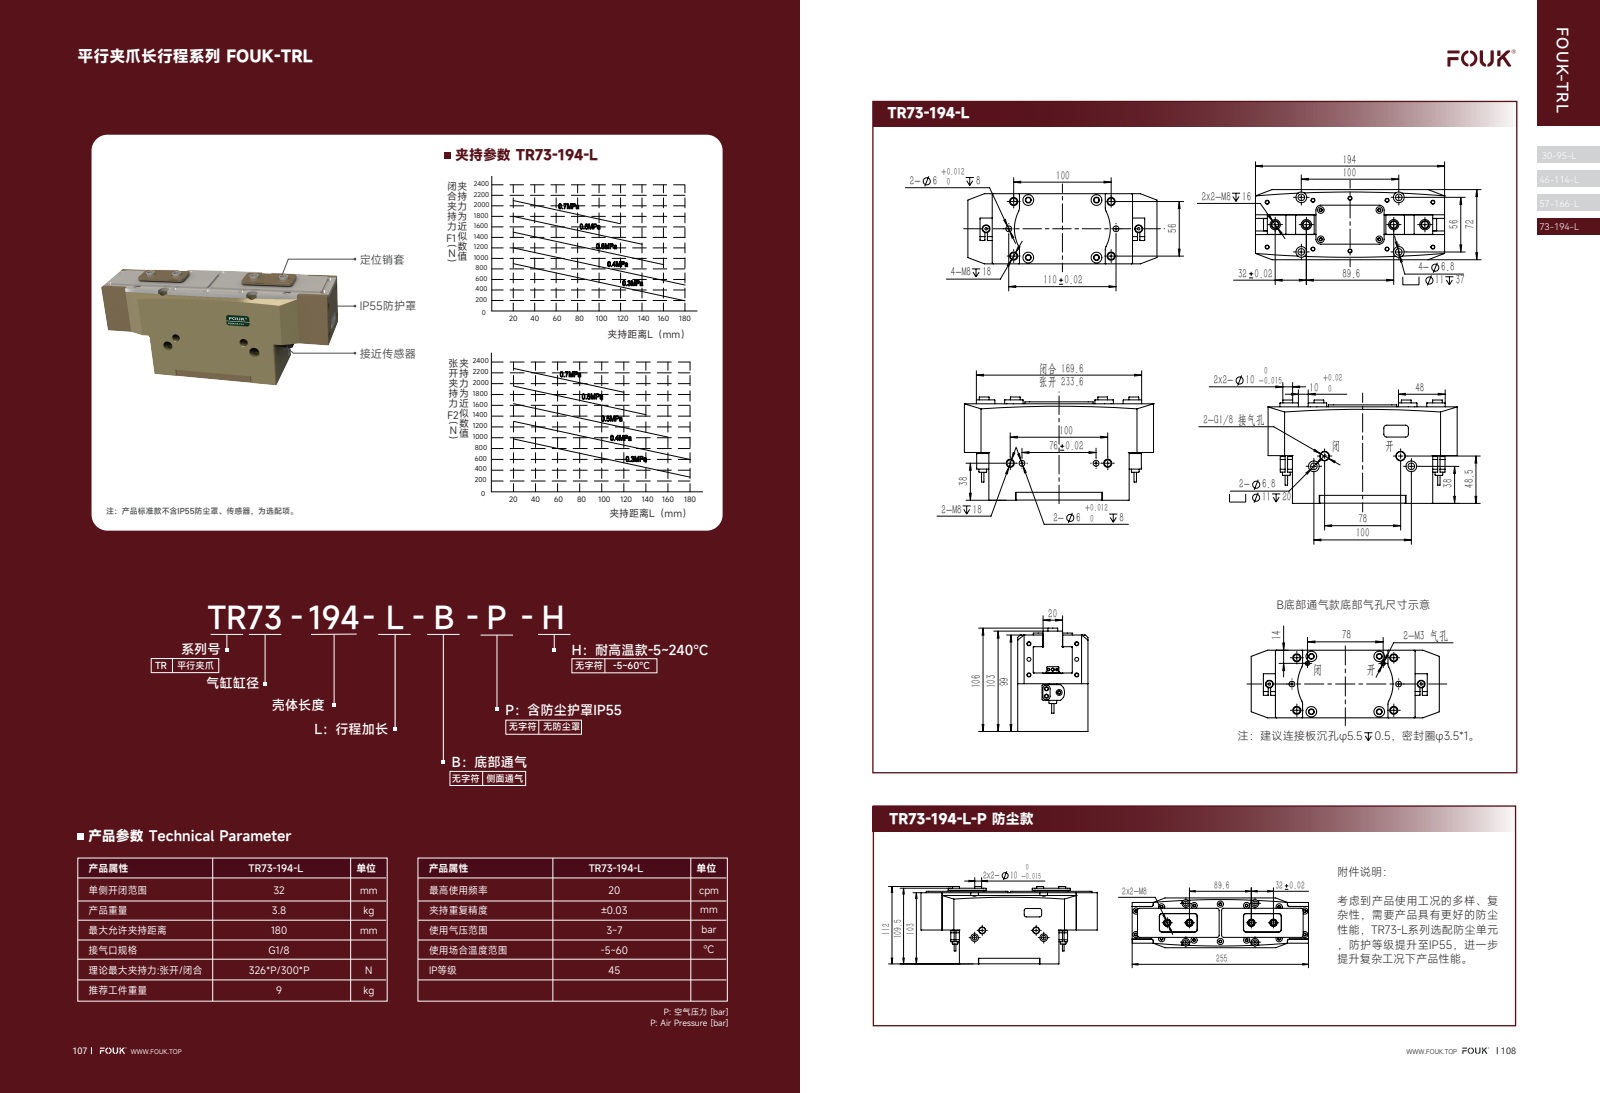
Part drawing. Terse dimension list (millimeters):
name: 25x12-R3; TR73-194-L
written by: SolidWorks 2018 (CONFIG_CONTROL_DESIGN)
unit: mm
bodies: 20 solids, 1367 faces (621 planar, 355 cylindrical, 391 other)
size: 194 × 106 × 72
volume: 1 134 000 mm³; area: 178 132 mm²
holes: 17× ⌀3.3, 10× ⌀6.8, 8× ⌀2.5, 6× ⌀8, 6× ⌀10, 6× ⌀11, 5× ⌀6, 4× ⌀3.4, 3× ⌀4.2, 2× ⌀2.05, 2× ⌀2.7, 2× ⌀4
bosses: 2× ⌀3.8, 2× ⌀2.5, 2× ⌀2, 1× ⌀2.6, 1× ⌀1.8
rounds: 18× R0.12, 12× R0.12, 8× R3, 5× R0.3, 4× R0.8, 4× R5, 4× R7, 4× R7.15
face distances: 16, 56, 72, 90.8, 39, 51.8, 40, 12, 27, 78.8
hole spacings: 47.42, 12.37, 12.81, 16, 21.07, 23.85, 23.96, 23.97
